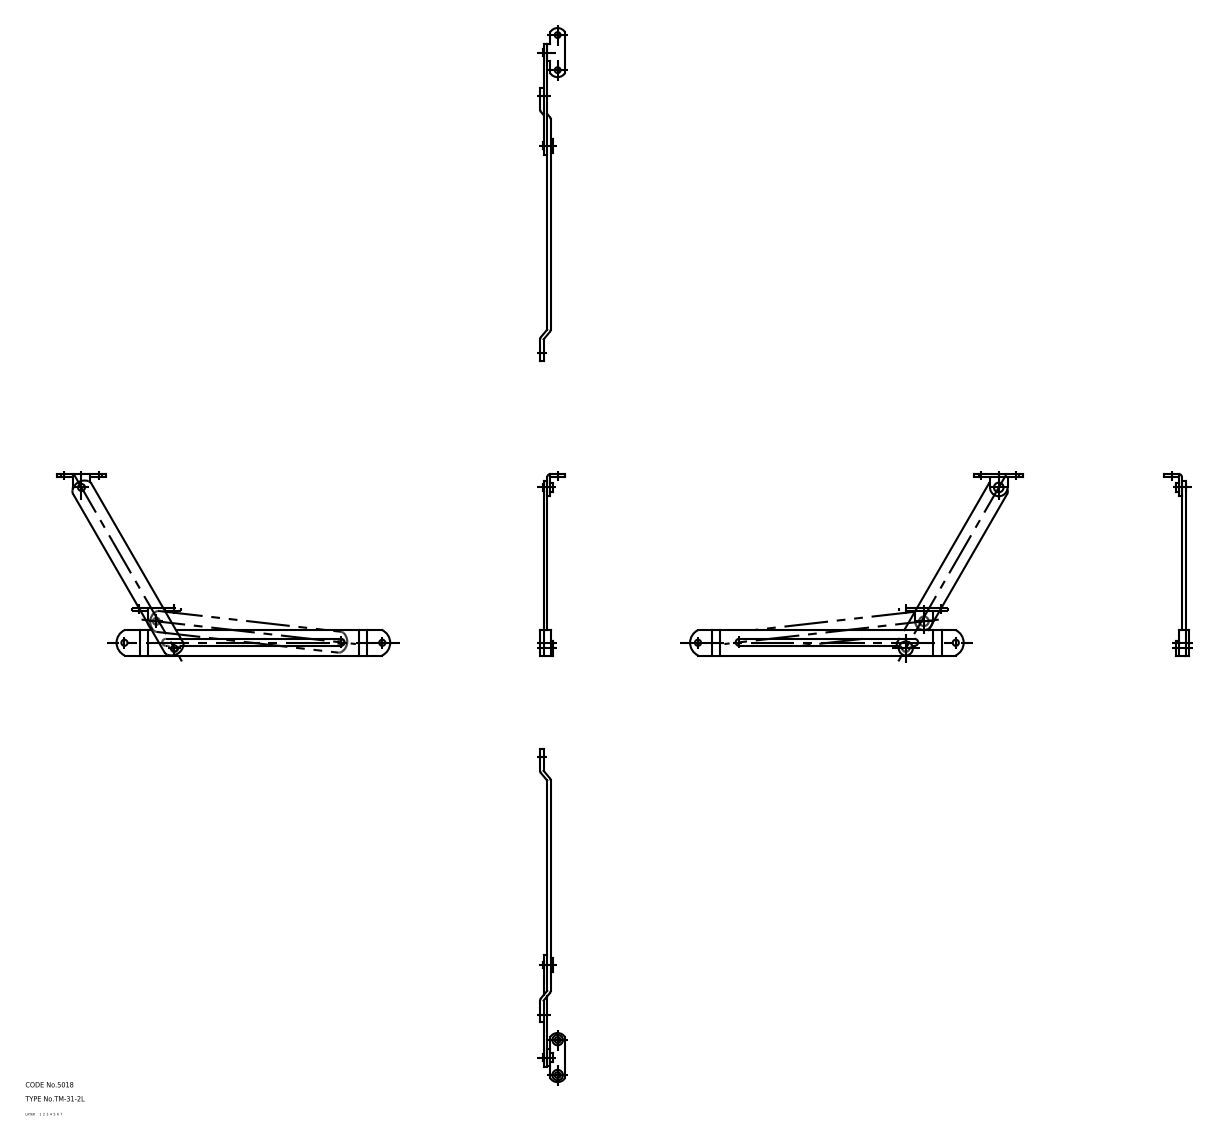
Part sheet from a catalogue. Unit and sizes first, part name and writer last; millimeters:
Units: millimetres
Overall size (bounding box): 190.5 × 103.4 × 14.3
Volume: 6 954 mm³ · Surface area: 9 086 mm²
Bodies: 5 solids, 89 faces (0 planar, 0 cylindrical, 89 other)
Part name (STEP PRODUCT): rivet_B; rivet_A; bracket; arm_B (+2 more)
STEP written by: CADfix (AUTOMOTIVE_DESIGN)
